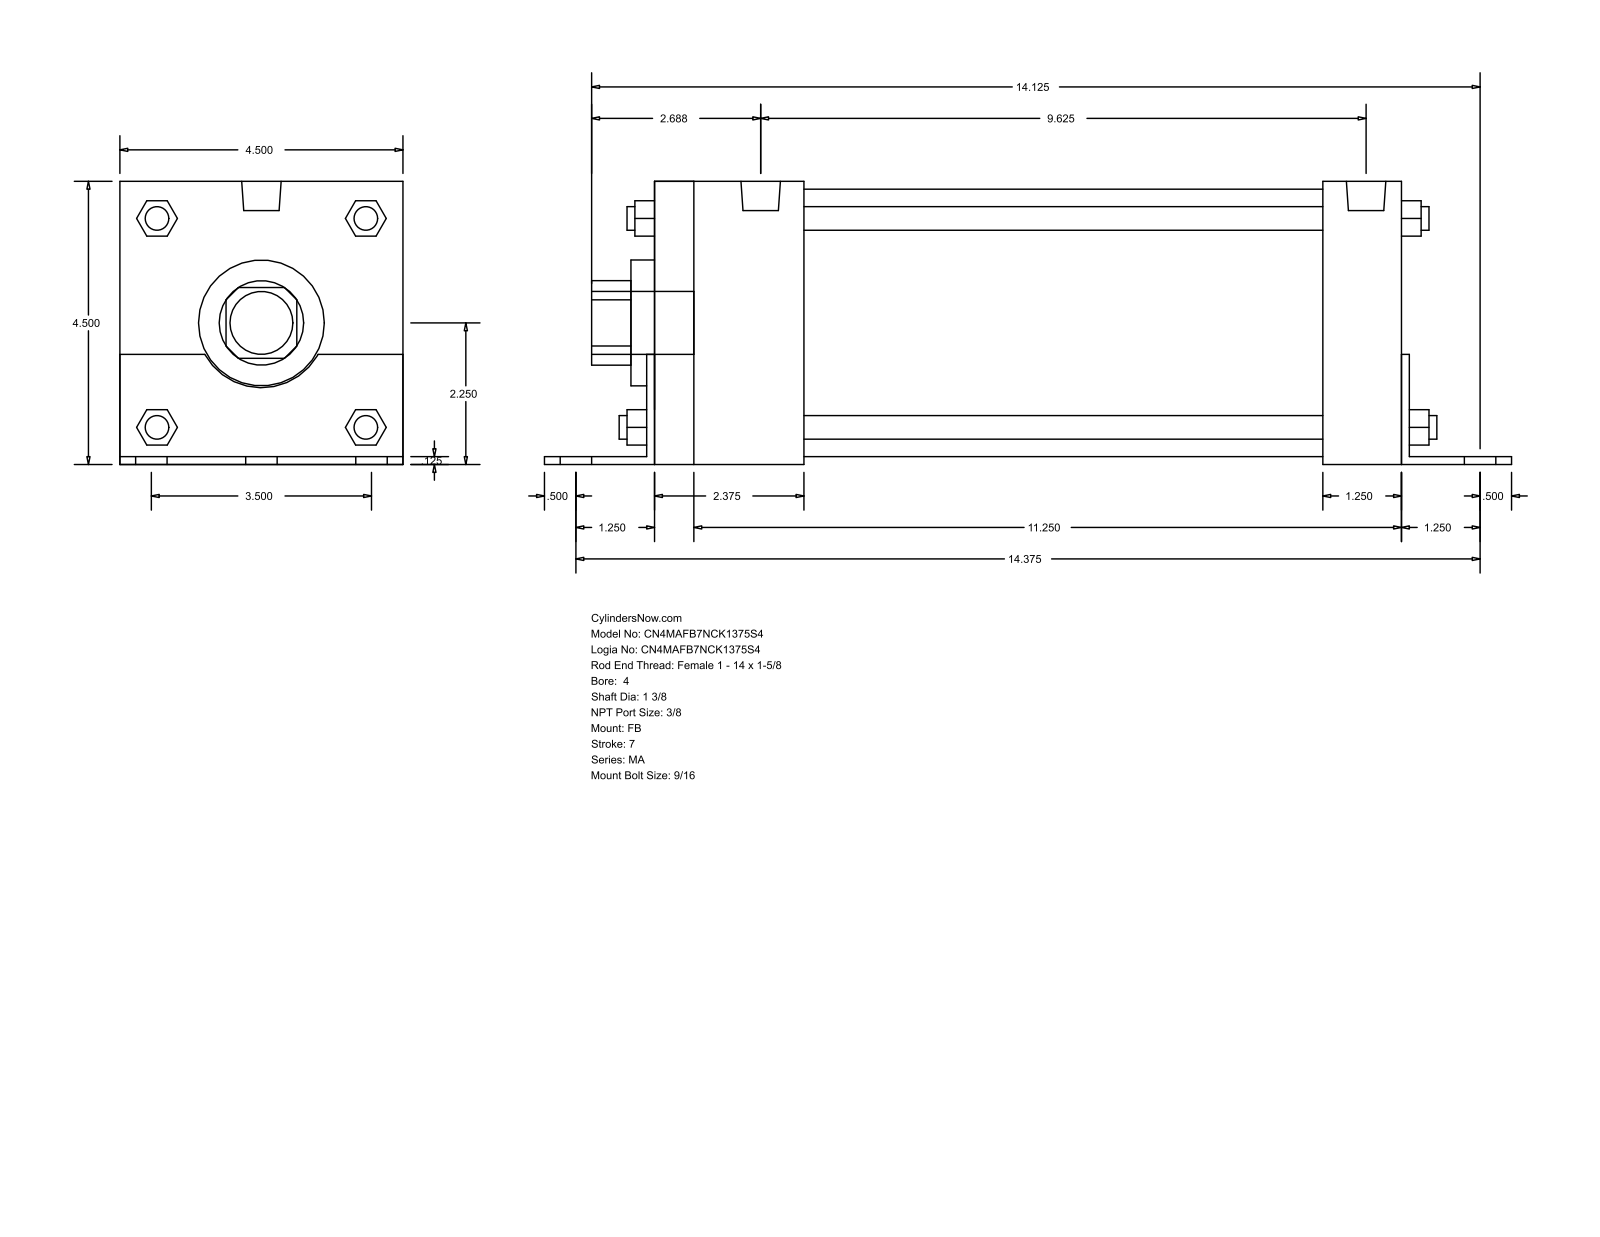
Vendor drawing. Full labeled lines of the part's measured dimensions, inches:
Part name (STEP PRODUCT): MA_FB__0400_1.375
STEP written by: GSSL Pune (CONFIG_CONTROL_DESIGN)
Units: inches
Bodies: 0 solids, 140 faces (105 planar, 35 cylindrical, 0 other)
Overall size (bounding box): 15.375 × 4.502 × 4.5
Round holes (diameter × count): ⌀1.375 ×1, ⌀2 ×1, ⌀4.25 ×1
Round bosses / shafts (diameter × count): ⌀0.563 ×6, ⌀0.437 ×4, ⌀0.375 ×4, ⌀0.627 ×2, ⌀1 ×1
Partial cylindrical surfaces — rounded edges, fillets, slot ends (radius × count): R0.672 ×1, R1.03 ×1
Main face-to-face distances: 4.5, 0.125, 4.502, 0.123, 4.377, 11.875, 0.125, 12, 1.375, 2.375
